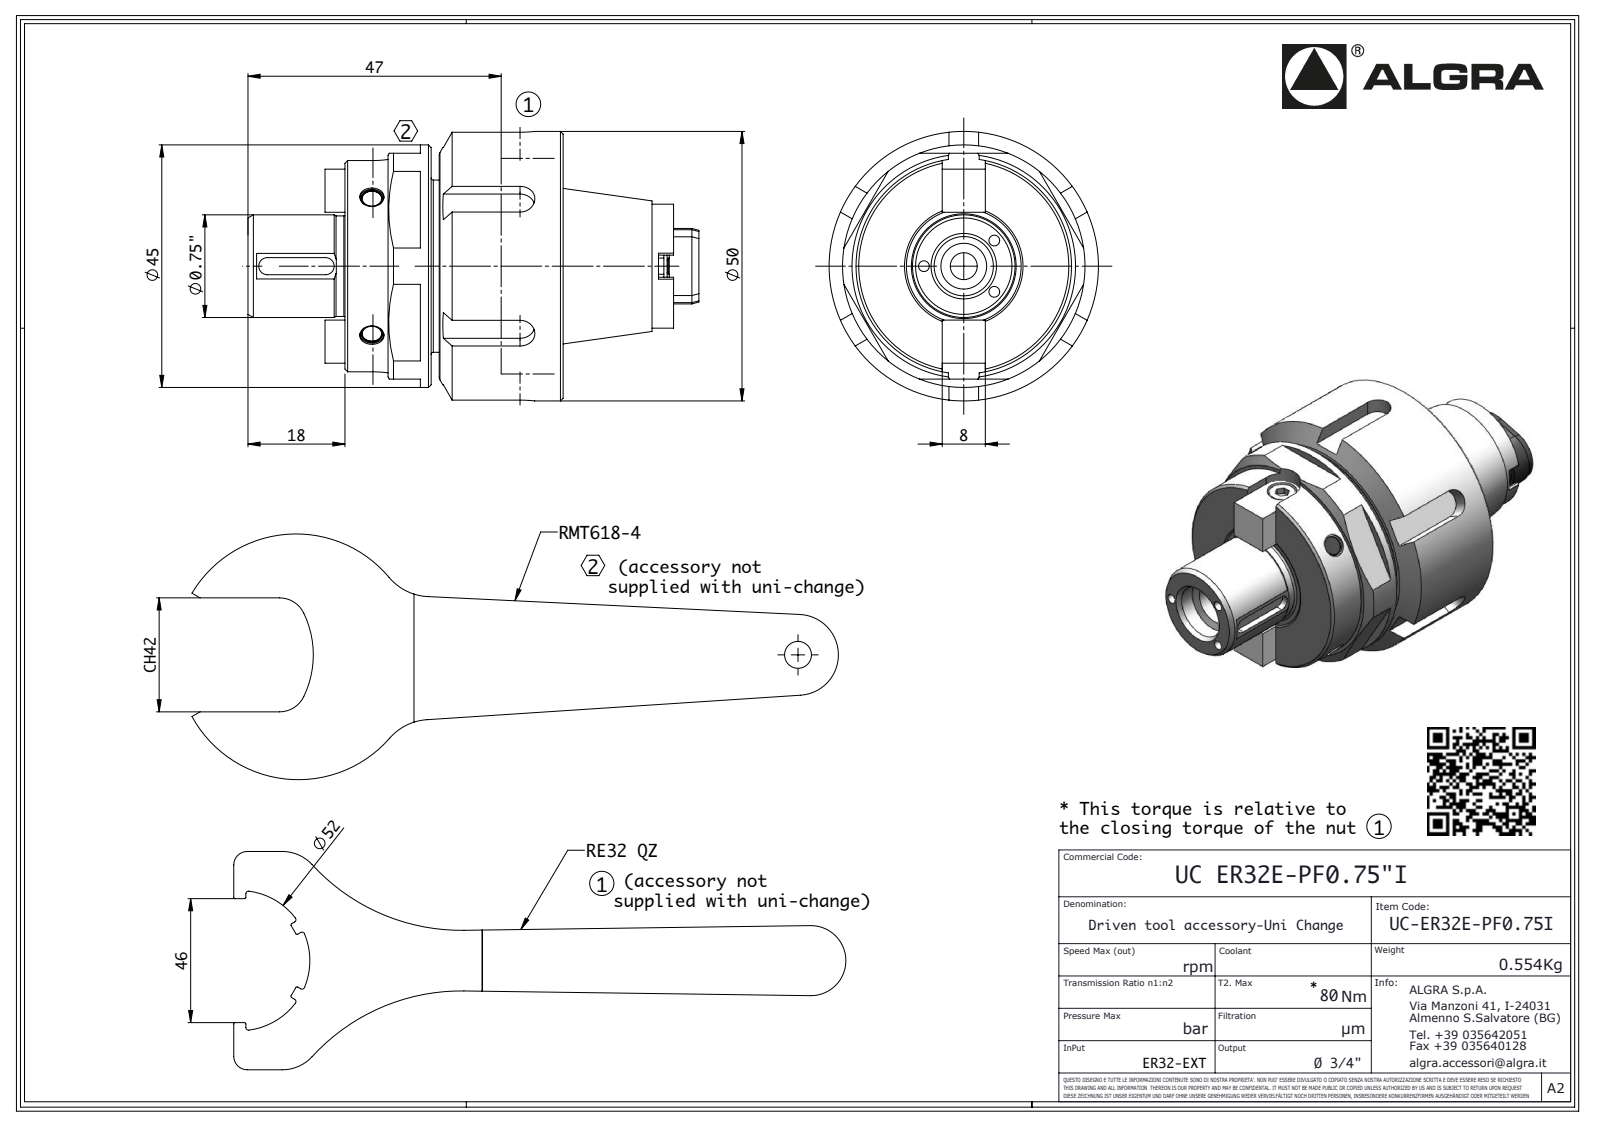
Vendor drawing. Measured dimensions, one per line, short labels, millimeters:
name: UC-ER32E-PF0.75I
written by: SolidWorks 2016 (AUTOMOTIVE_DESIGN)
unit: mm
bodies: 0 solids, 172 faces (95 planar, 51 cylindrical, 26 other)
size: 79 × 50 × 50
holes: 3× ⌀2, 3× ⌀4, 3× ⌀4.5, 2× ⌀2.5, 1× ⌀5, 1× ⌀6, 1× ⌀8.5, 1× ⌀11, 1× ⌀38.5, 1× ⌀40.5
bosses: 1× ⌀50, 1× ⌀45, 1× ⌀40, 1× ⌀23, 1× ⌀19.05, 1× ⌀18.65, 1× ⌀5.5
rounds: 8× R0.3, 3× R2.75, 2× R1.59, 2× R5.64, 1× R4, 1× R7
face distances: 16, 24.5, 40.5, 8, 1.05, 42.95, 9.5, 13.5, 11, 27
hole spacings: 7.4, 5.02, 7.25, 13.77, 13.91, 9.52, 14.5, 14.65
